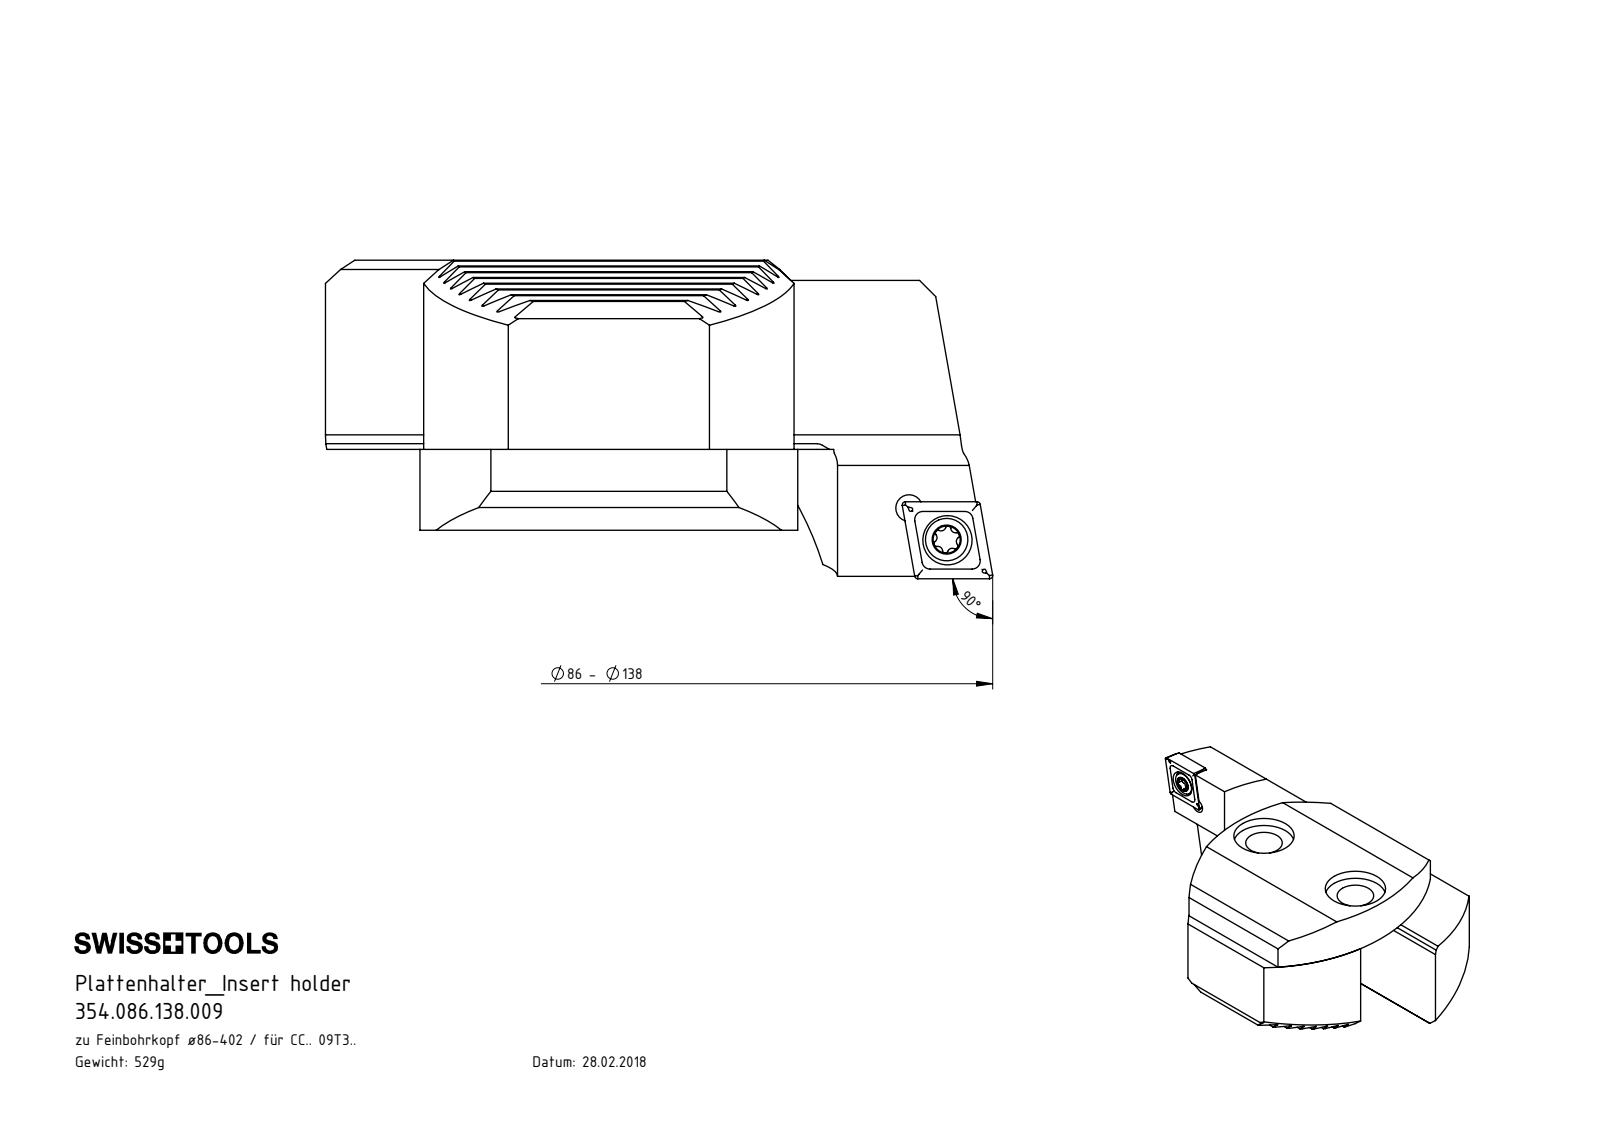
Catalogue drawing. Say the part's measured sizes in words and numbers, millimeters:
The part is named "354.086.138.009; F00-WCB.086.003_A; F00-WCB.086.002_A; F00-WCB.086.001 (+3 more)". Its 3-D file was written by "SolidWorks 2017 (CONFIG_CONTROL_DESIGN)". It is 5 solids with 442 faces: 264 planar, 59 cylindrical and 119 other. Overall it measures 82.57 by 55 by 39.4 millimeters. Its volume is 67 401 cubic millimeters and its surface area 19 323 square millimeters. Round holes: 2 of diameter 3.3, 2 of diameter 8.5, 2 of diameter 14, 1 of diameter 4.4, 1 of diameter 6.1. Round bosses or shafts: 1 of diameter 5.25, 1 of diameter 4. Partial cylindrical surfaces (rounded edges, fillets, slot ends): 16 of radius 0.2, 7 of radius 40, 6 of radius 0.34, 6 of radius 0.59, 1 of radius 0.8. The main face-to-face distances are 2.38, 21.3, 33.7, 4.76, 12.4, 10, 7.15, 9.53, 11.91, 7.14. The hole center spacings are 6.07, 6.2, 30.
